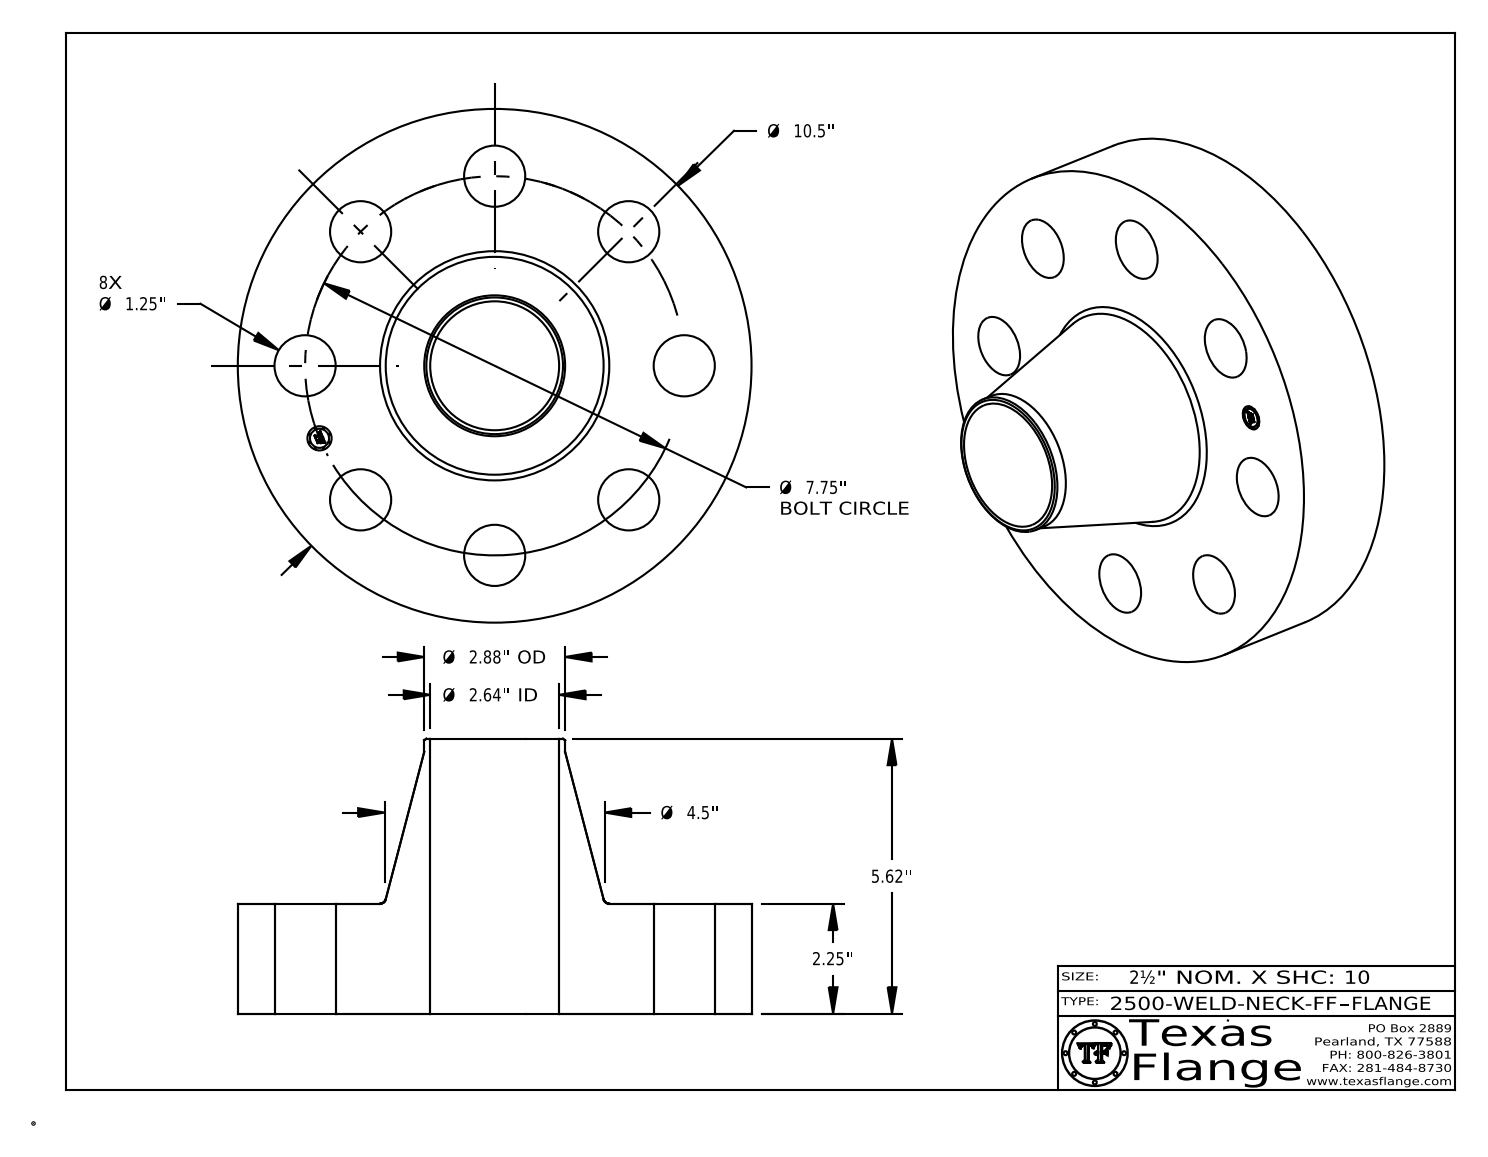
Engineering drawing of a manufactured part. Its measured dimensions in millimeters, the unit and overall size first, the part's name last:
Units: millimetres
Overall size (bounding box): 266.7 × 266.7 × 142.7
Round holes (diameter × count): ⌀31.8 ×8, ⌀12.6 ×1, ⌀66.9 ×1
Round bosses / shafts (diameter × count): ⌀0.8 ×8, ⌀266.7 ×1, ⌀73.2 ×1, ⌀9.9 ×1
Main face-to-face distances: 57.2, 142.7, 85.6, 56.8, 0.4, 86, 3.8, 3.7, 0.7, 2.4
Hole centre spacings: 75.3, 98.4, 139.2, 181.9, 196.9, 193.1, 38.4, 38.4
Volume: 2 910 000 mm³ · Surface area: 234 700 mm²
Bodies: 1 solid, 416 faces (368 planar, 42 cylindrical, 6 other)
Part name (STEP PRODUCT): 2500-WELD-NECK-FF
STEP written by: CATIA V5 STEP AP214 (AUTOMOTIVE_DESIGN)
